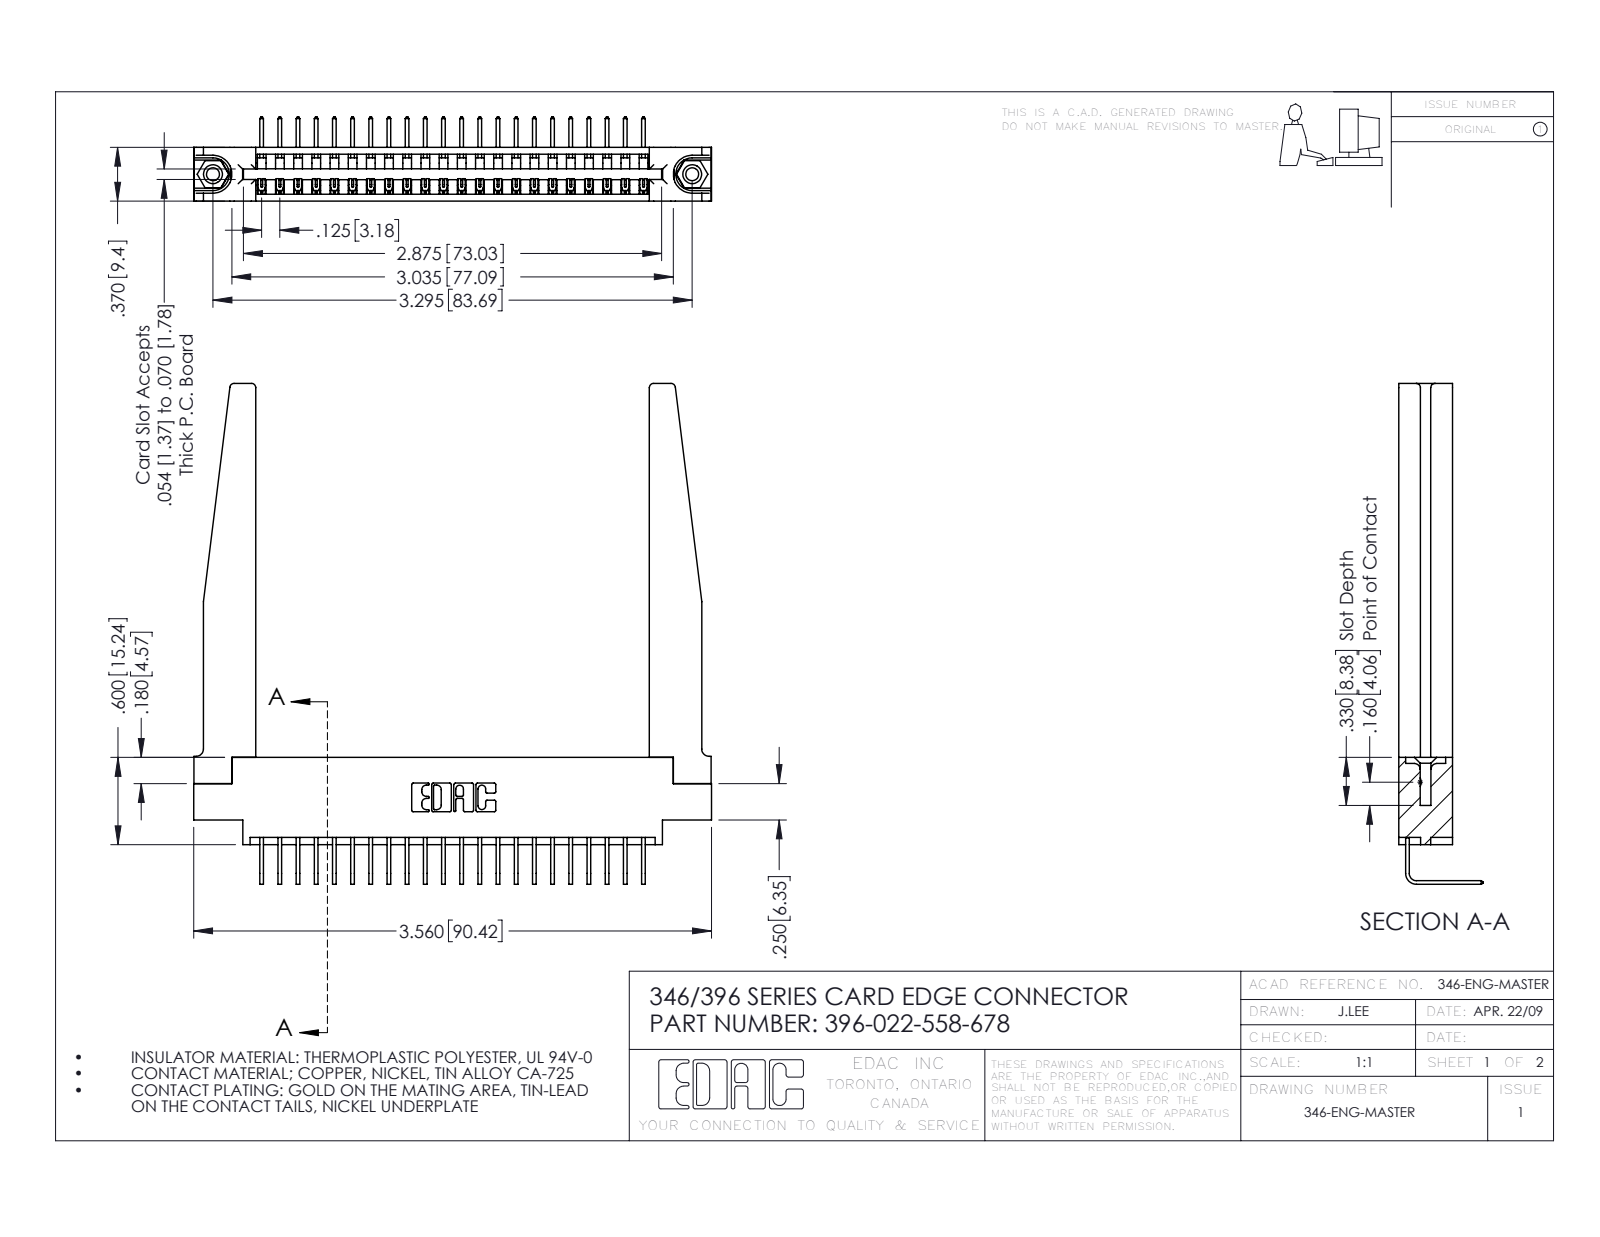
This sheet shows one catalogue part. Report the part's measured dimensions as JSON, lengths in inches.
{"part_name": "396-022-558-678; 346 Part_0.170 Offset - 0.156 Dia-TH; 345-250-001_345-250-001-102; 346-220-078_345-220-078 (+1 more)", "step_written_by": "SolidWorks 2016 (CONFIG_CONTROL_DESIGN)", "units": "inches", "bodies": {"solids": 27, "faces": 1680, "planar": 1146, "cylindrical": 482, "other": 52}, "overall_size": [3.56, 3.443, 0.58], "volume_in3": 0.936, "surface_area_in2": 27.07, "round_holes": [[0.089, 2], [0.125, 2], [0.156, 2], [0.064, 1]], "round_bosses_or_shafts": [[0.155, 2]], "partial_cylinders_radius": [[0.006, 44], [0.01, 22], [0.03, 8], [0.007, 6], [0.031, 6], [0.026, 3], [0.05, 3], [0.031, 2]], "face_to_face_distances": [0.37, 0.322, 0.072, 0.048, 0.148, 0.15, 0.25, 0.298, 0.025, 0.222], "hole_center_spacings": [0.246, 3.087, 3.295]}
